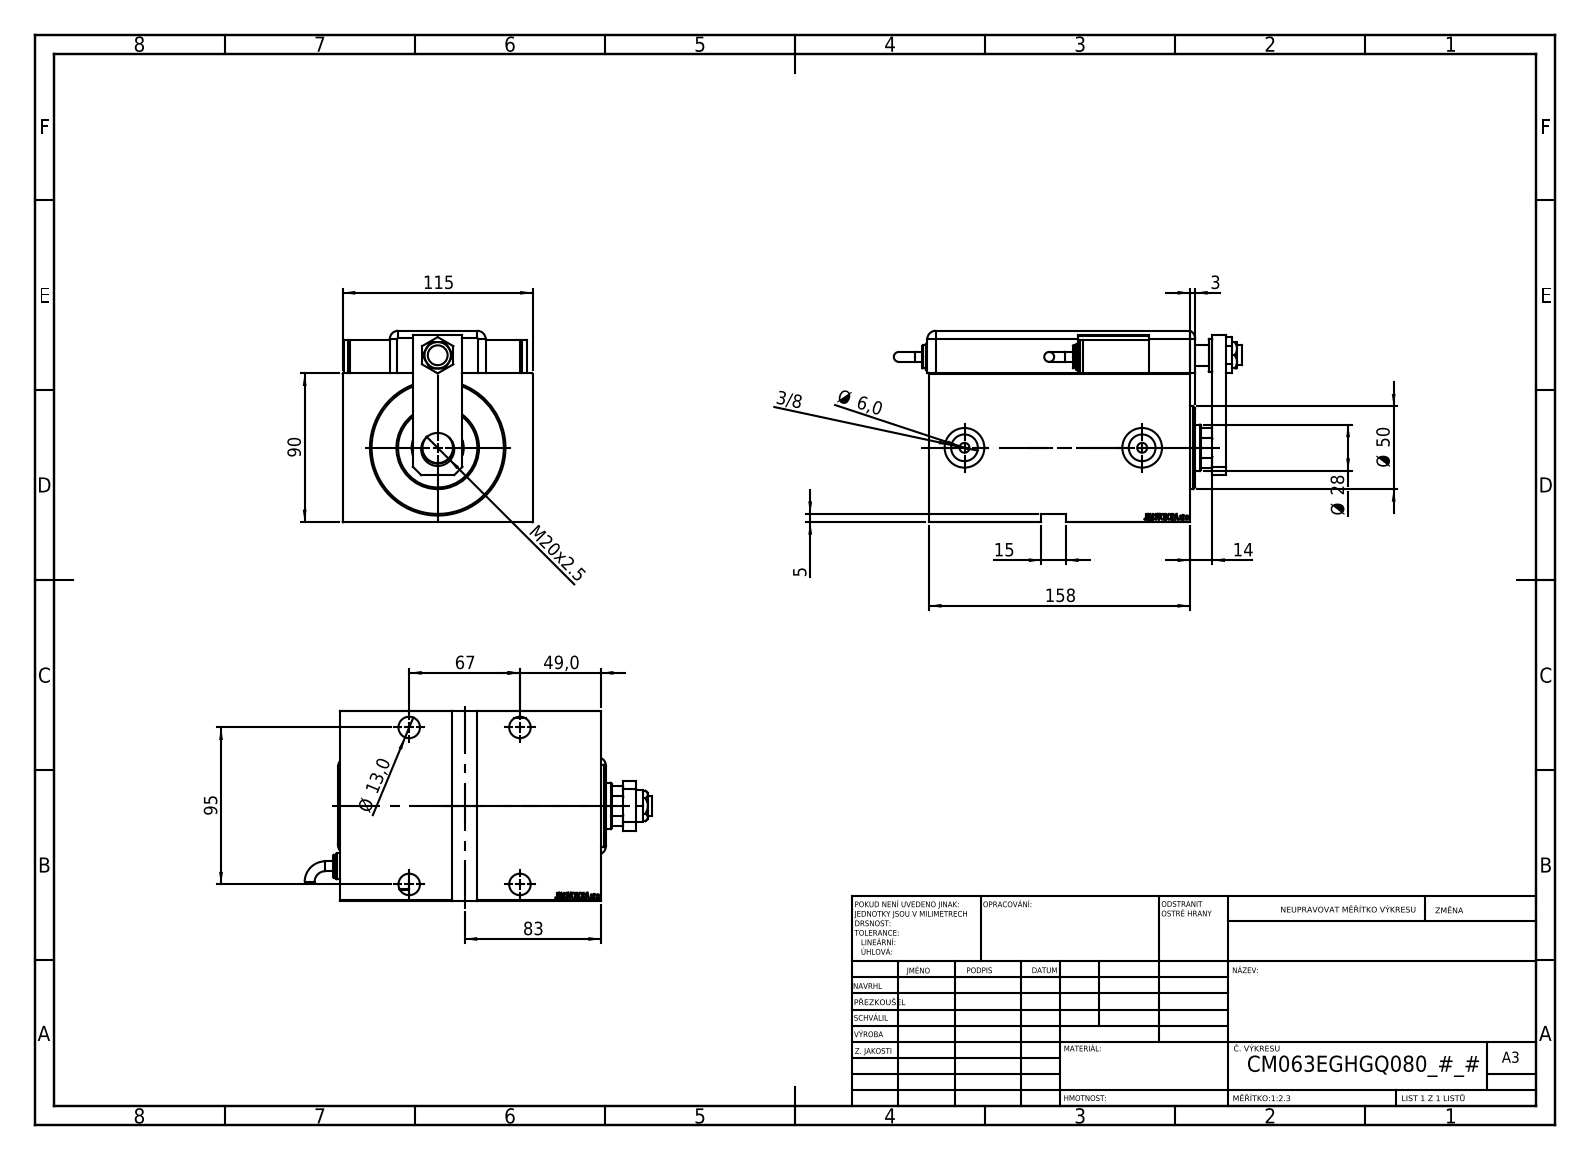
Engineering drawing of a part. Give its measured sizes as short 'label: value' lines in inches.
name: V450CM_E_VCP; SWITCH Q; ZARAZKA_Q; NUT_D19 (+7 more)
written by: SolidWorks 2019 (CONFIG_CONTROL_DESIGN)
unit: in
bodies: 13 solids, 1240 faces (616 planar, 107 cylindrical, 517 other)
size: 8.286 × 4.559 × 4.528
volume: 94.22 in³; area: 375.7 in²
holes: 5× ⌀0.512, 4× ⌀0.748, 2× ⌀0.157, 2× ⌀0.236, 2× ⌀0.315, 2× ⌀0.637, 2× ⌀0.945, 1× ⌀0.472, 1× ⌀0.551, 1× ⌀0.728, 1× ⌀0.787, 1× ⌀1.102
bosses: 3× ⌀0.787, 2× ⌀0.63, 2× ⌀0.551, 2× ⌀0.236, 1× ⌀2.559, 1× ⌀1.969
rounds: 9× R0.197, 1× R0.394, 1× R0.531
face distances: 3.543, 4.528, 0.118, 6.22, 4.559, 1.016, 0.689, 5.531, 1.122, 0.728
hole spacings: 2.202, 2.638, 2.792, 3.74, 4.52, 4.577, 4.834, 0.039
